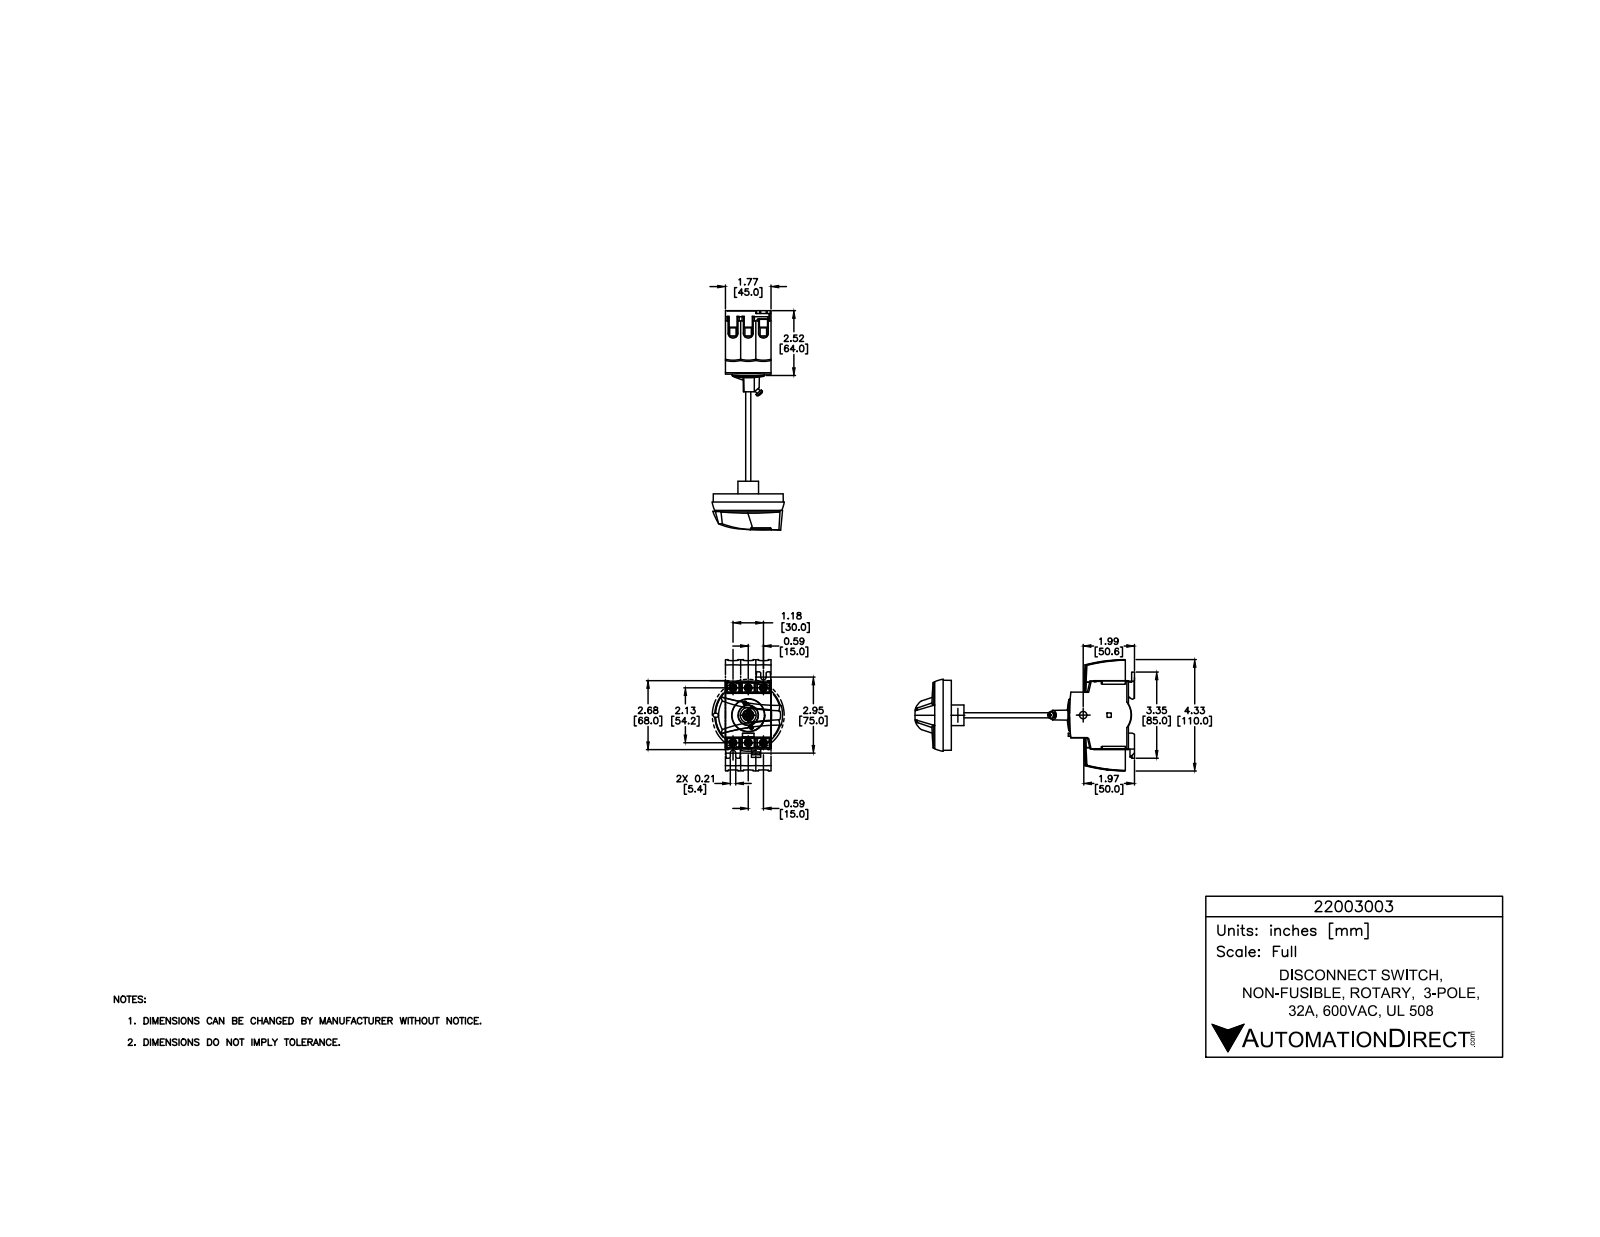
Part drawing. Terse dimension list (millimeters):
name: 22003003-UL
written by: SolidWorks 2021 (CONFIG_CONTROL_DESIGN)
unit: mm
bodies: 1 solid, 463 faces (389 planar, 50 cylindrical, 24 other)
size: 85 × 65.3 × 45
volume: 155 600 mm³; area: 25 950 mm²
holes: 6× ⌀6.6, 1× ⌀7.2, 1× ⌀31.6
rounds: 13× R0.3, 5× R0.5, 4× R4.2, 3× R1, 2× R2.7, 1× R3.3, 1× R9, 1× R9.4
face distances: 45, 11, 56, 54.8, 67, 57.9, 15, 65.8, 1.2, 9.8
hole spacings: 15, 31, 56.2, 54.2, 27.1, 30, 62
